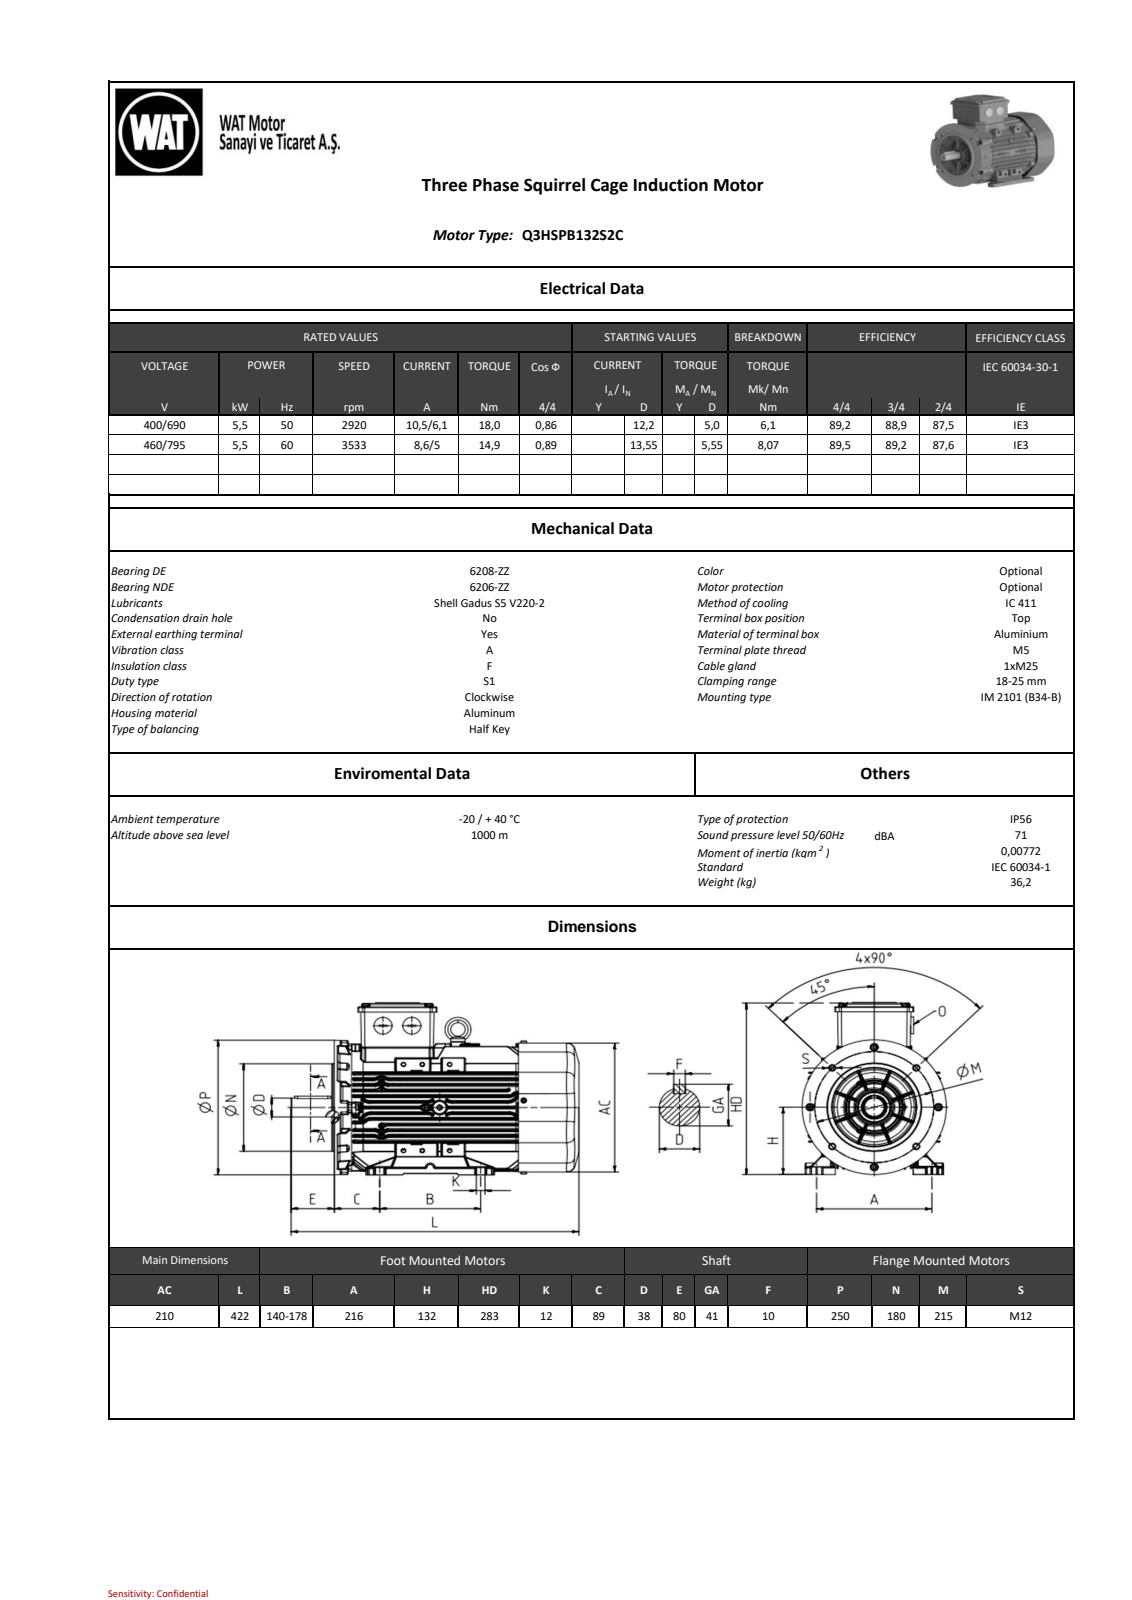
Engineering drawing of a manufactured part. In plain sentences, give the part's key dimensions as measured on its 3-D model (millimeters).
The part is named "Ar311510F805543y". Its 3-D file was written by "SIEMENS PLM Software NX 9.0 (AUTOMOTIVE_DESIGN)". It is 0 solids with 12315 faces: 2512 planar, 3763 cylindrical and 6040 other. Overall it measures 422 by 282.97 by 250.56 millimeters. Round holes: 6 of diameter 12, 5 of diameter 10.3, 4 of diameter 4.92, 4 of diameter 8.3, 3 of diameter 6.5, 3 of diameter 6.65, 2 of diameter 27.8, 1 of diameter 4, 1 of diameter 4.72, 1 of diameter 8, 1 of diameter 13, 1 of diameter 30. Round bosses or shafts: 12 of diameter 8, 4 of diameter 20, 4 of diameter 14.8, 4 of diameter 13, 4 of diameter 11.8, 4 of diameter 10, 4 of diameter 6, 2 of diameter 4. Partial cylindrical surfaces (rounded edges, fillets, slot ends): 989 of radius 0.5, 549 of radius 0.8, 532 of radius 1, 240 of radius 2, 44 of radius 3, 30 of radius 0.38, 25 of radius 0.3, 12 of radius 0.2. The main face-to-face distances are 1, 11, 5, 21.5, 35.96, 10.99, 24.97, 9.67, 111.37, 92.91. The hole center spacings are 40, 78.72, 188.51, 96.5, 110, 72.62, 78.73, 107.49.
